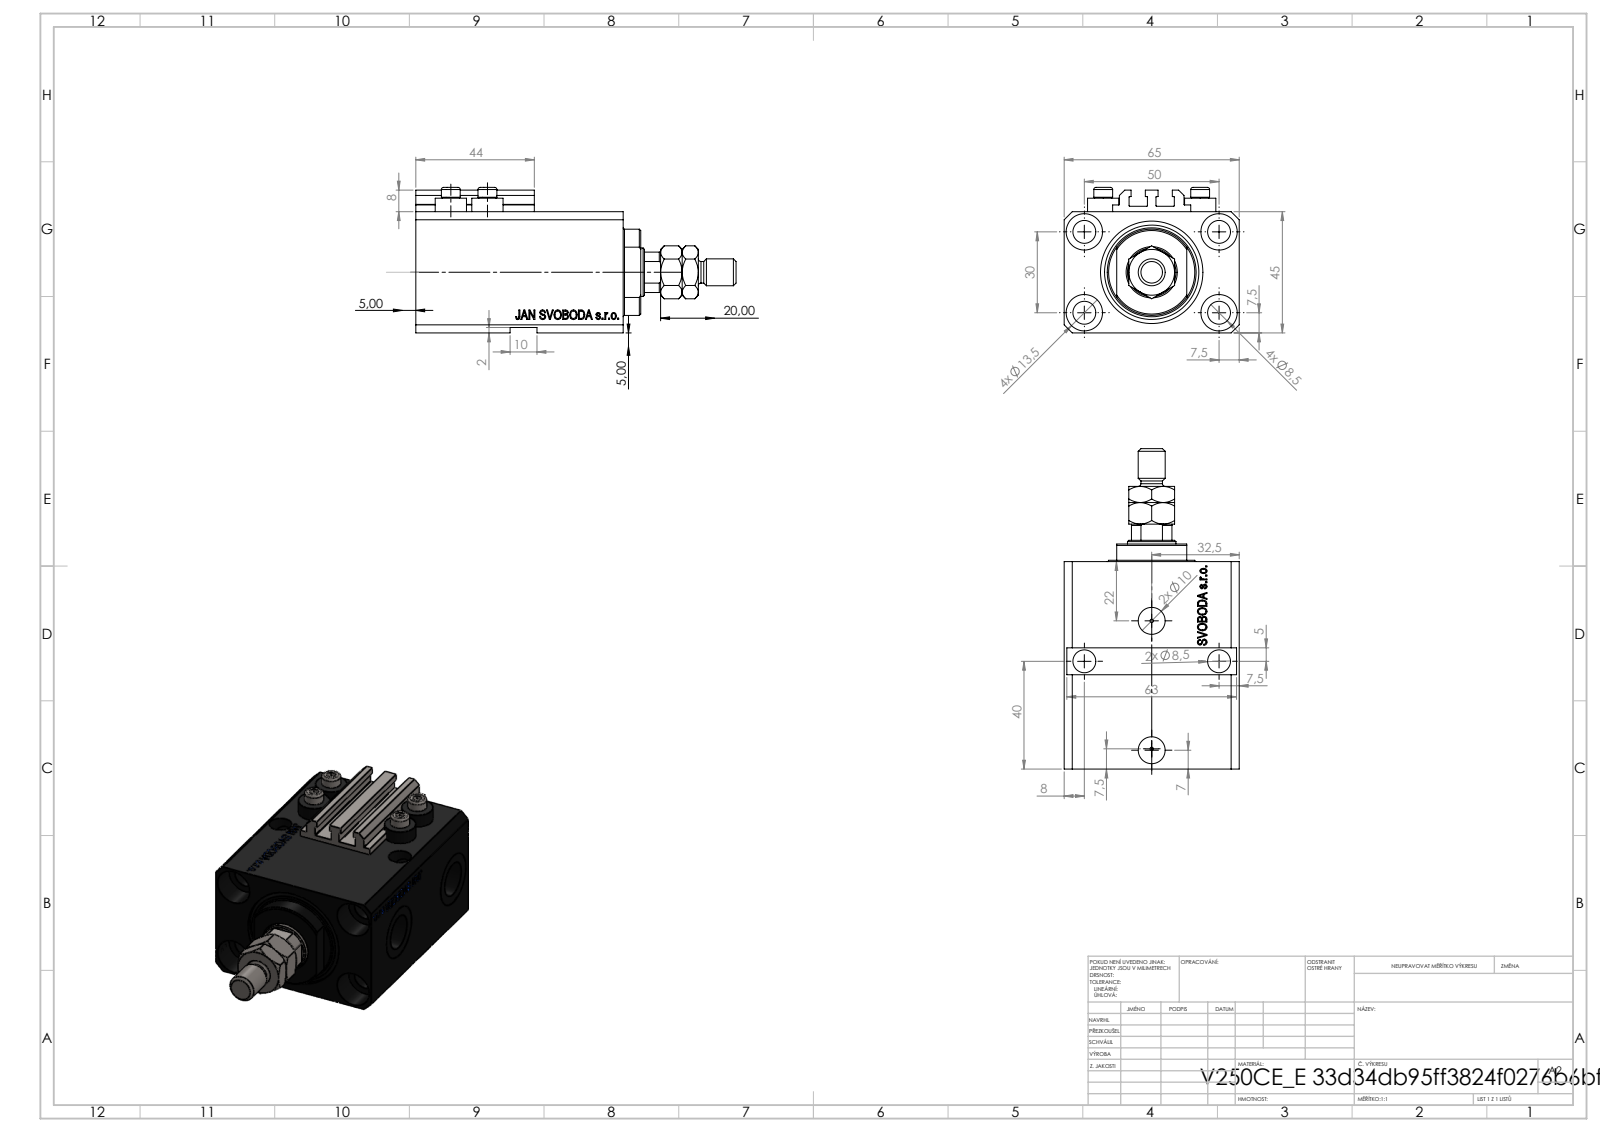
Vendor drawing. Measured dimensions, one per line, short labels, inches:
name: V250CE_C_VCP; V250CE_VC_E; V250CE_E_Body; MTA (+1 more)
written by: SolidWorks 2019 (CONFIG_CONTROL_DESIGN)
unit: in
bodies: 9 solids, 1116 faces (526 planar, 130 cylindrical, 460 other)
size: 4.685 × 2.559 × 2.126
volume: 12.46 in³; area: 94.43 in²
holes: 7× ⌀0.335, 4× ⌀0.049, 4× ⌀0.157, 4× ⌀0.531, 2× ⌀0.394, 2× ⌀0.518, 2× ⌀0.787, 1× ⌀0.709, 1× ⌀0.984, 1× ⌀1.496
bosses: 4× ⌀0.457, 4× ⌀0.276, 1× ⌀0.394, 1× ⌀0.315
rounds: 10× R0.008, 1× R0.335, 1× R0.63
face distances: 1.772, 2.559, 0.551, 2.48, 3.031, 0.079, 0.272, 2.209, 2.76, 0.807
hole spacings: 1.148, 1.969, 0.535, 0.595, 0.741, 0.747, 1.032, 1.048
